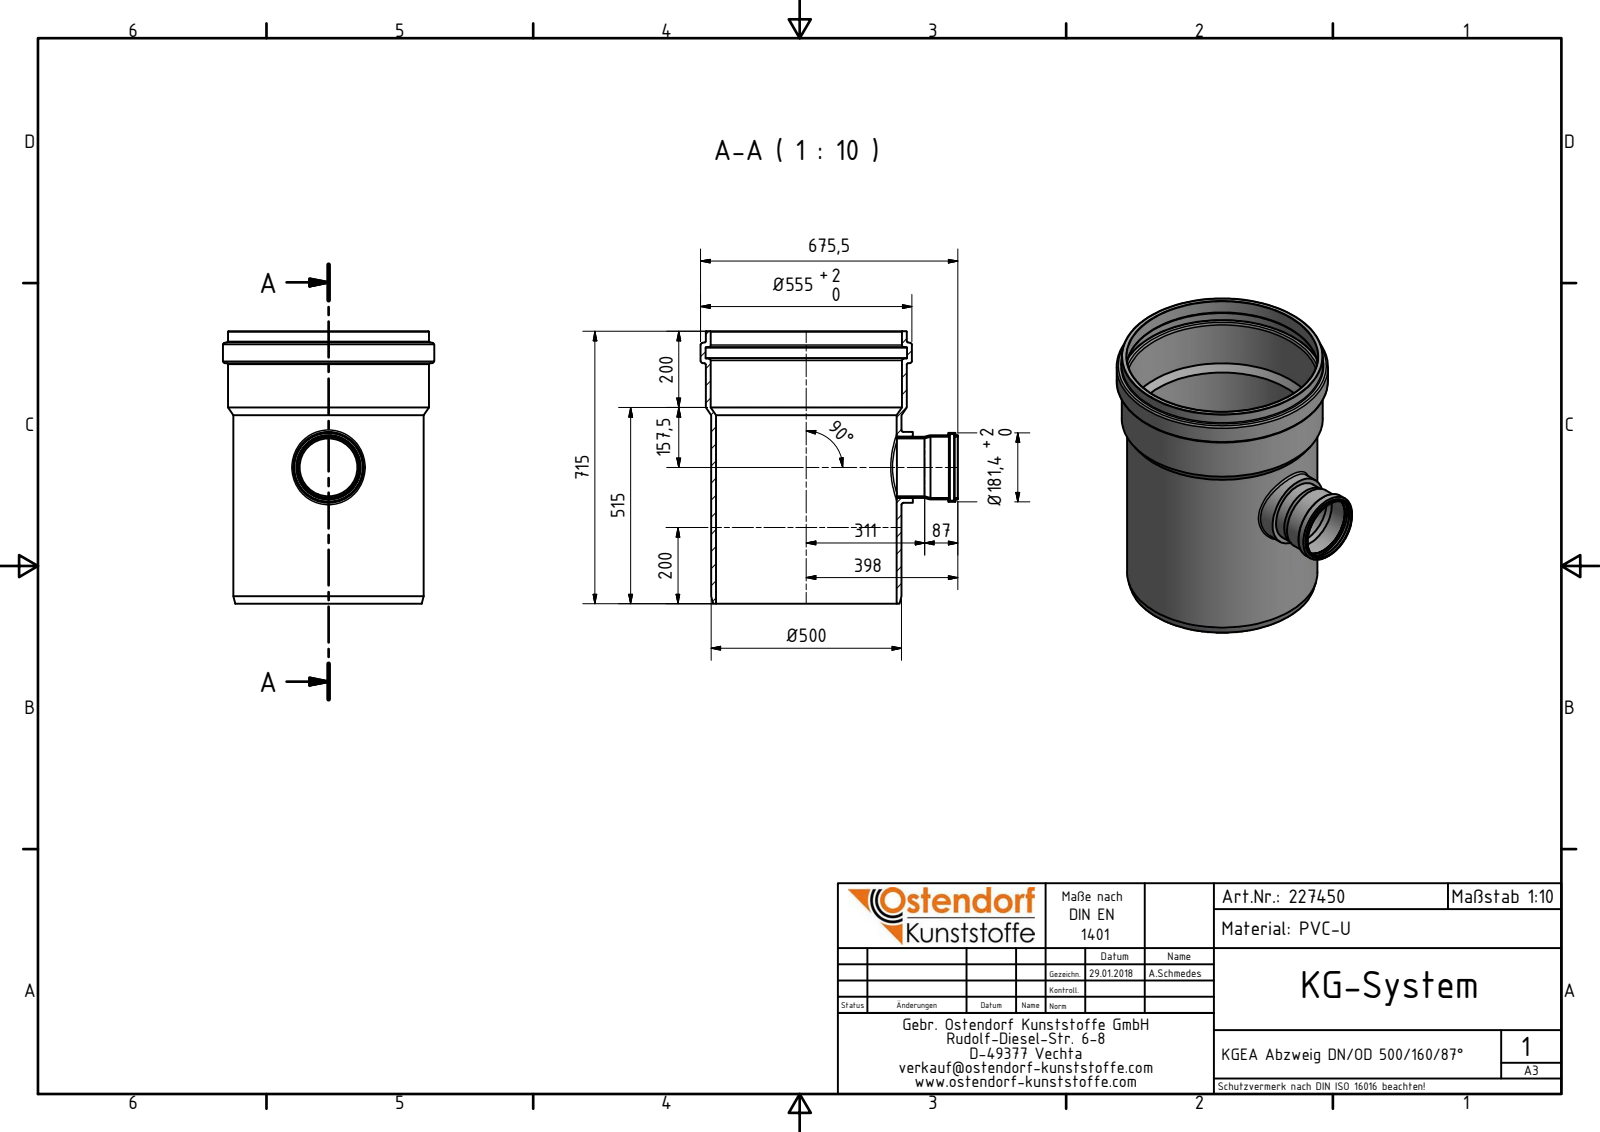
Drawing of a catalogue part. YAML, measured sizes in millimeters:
part_name: "227450 KGEA Abzweig DN_OD 500_160_87°; 227450 KGEA Abzweig DN_OD 500_160_87° Abzweig"
step_written_by: "Autodesk Inventor 2016 (AUTOMOTIVE_DESIGN)"
units: millimeters
bodies: {solids: 2, faces: 60, planar: 6, cylindrical: 19, other: 35}
overall_size: [715, 675.5, 555]
volume: 15260000
surface_area: 2525000
round_holes:
  - {diameter: 152.3, count: 1}
  - {diameter: 160.3, count: 1}
  - {diameter: 160.7, count: 1}
  - {diameter: 161.1, count: 1}
  - {diameter: 174.4, count: 1}
  - {diameter: 474, count: 1}
  - {diameter: 502, count: 1}
  - {diameter: 529, count: 1}
round_bosses_or_shafts:
  - {diameter: 555, count: 1}
  - {diameter: 528, count: 1}
  - {diameter: 500, count: 1}
  - {diameter: 186.3, count: 1}
  - {diameter: 181.4, count: 1}
  - {diameter: 168.1, count: 1}
  - {diameter: 167.7, count: 1}
face_to_face_distances: [715, 42, 118, 160, 23.61, 94.39, 136.39]
